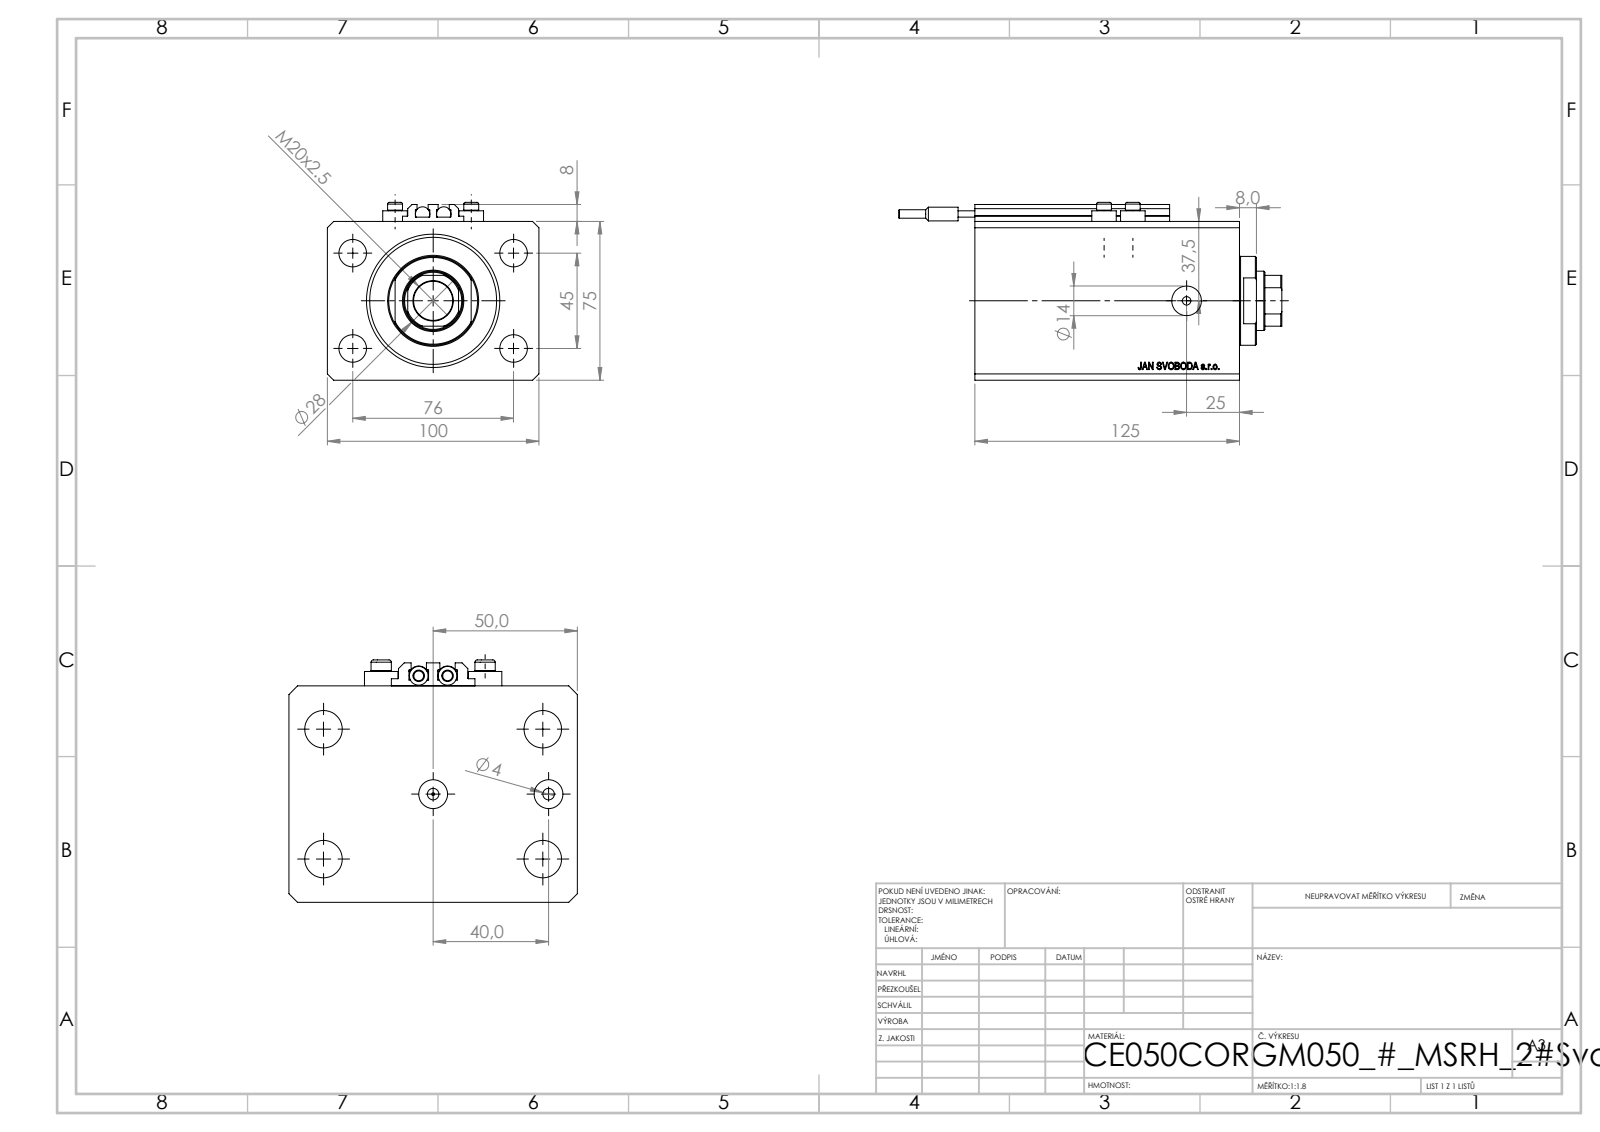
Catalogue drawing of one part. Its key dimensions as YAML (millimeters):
part_name: "ALLEN BOLT V250CE; V250CE_C_VCP; SWITCH_V250CE; V250CE_VC_C (+1 more)"
step_written_by: "SolidWorks 2019 (CONFIG_CONTROL_DESIGN)"
units: millimeters
bodies: {solids: 10, faces: 1090, planar: 536, cylindrical: 100, other: 454}
overall_size: [181, 100, 84]
volume: 823096
surface_area: 145792
round_holes:
  - {diameter: 4, count: 8}
  - {diameter: 13, count: 4}
  - {diameter: 10, count: 2}
  - {diameter: 14, count: 2}
  - {diameter: 1.25, count: 1}
  - {diameter: 18.5, count: 1}
  - {diameter: 28, count: 1}
  - {diameter: 50, count: 1}
  - {diameter: 63, count: 1}
round_bosses_or_shafts:
  - {diameter: 11.6, count: 4}
  - {diameter: 7, count: 4}
  - {diameter: 6.8, count: 2}
  - {diameter: 6.5, count: 2}
  - {diameter: 4, count: 2}
  - {diameter: 42, count: 1}
partial_cylinders:
  - {radius: 0.2, count: 10}
  - {radius: 13.5, count: 1}
face_to_face_distances: [75, 100, 125, 20, 11.9, 113.1, 105, 93.1, 2, 8]
hole_center_spacings: [44.16, 13.6, 22.59, 36, 38.48, 45, 76, 81.18]
